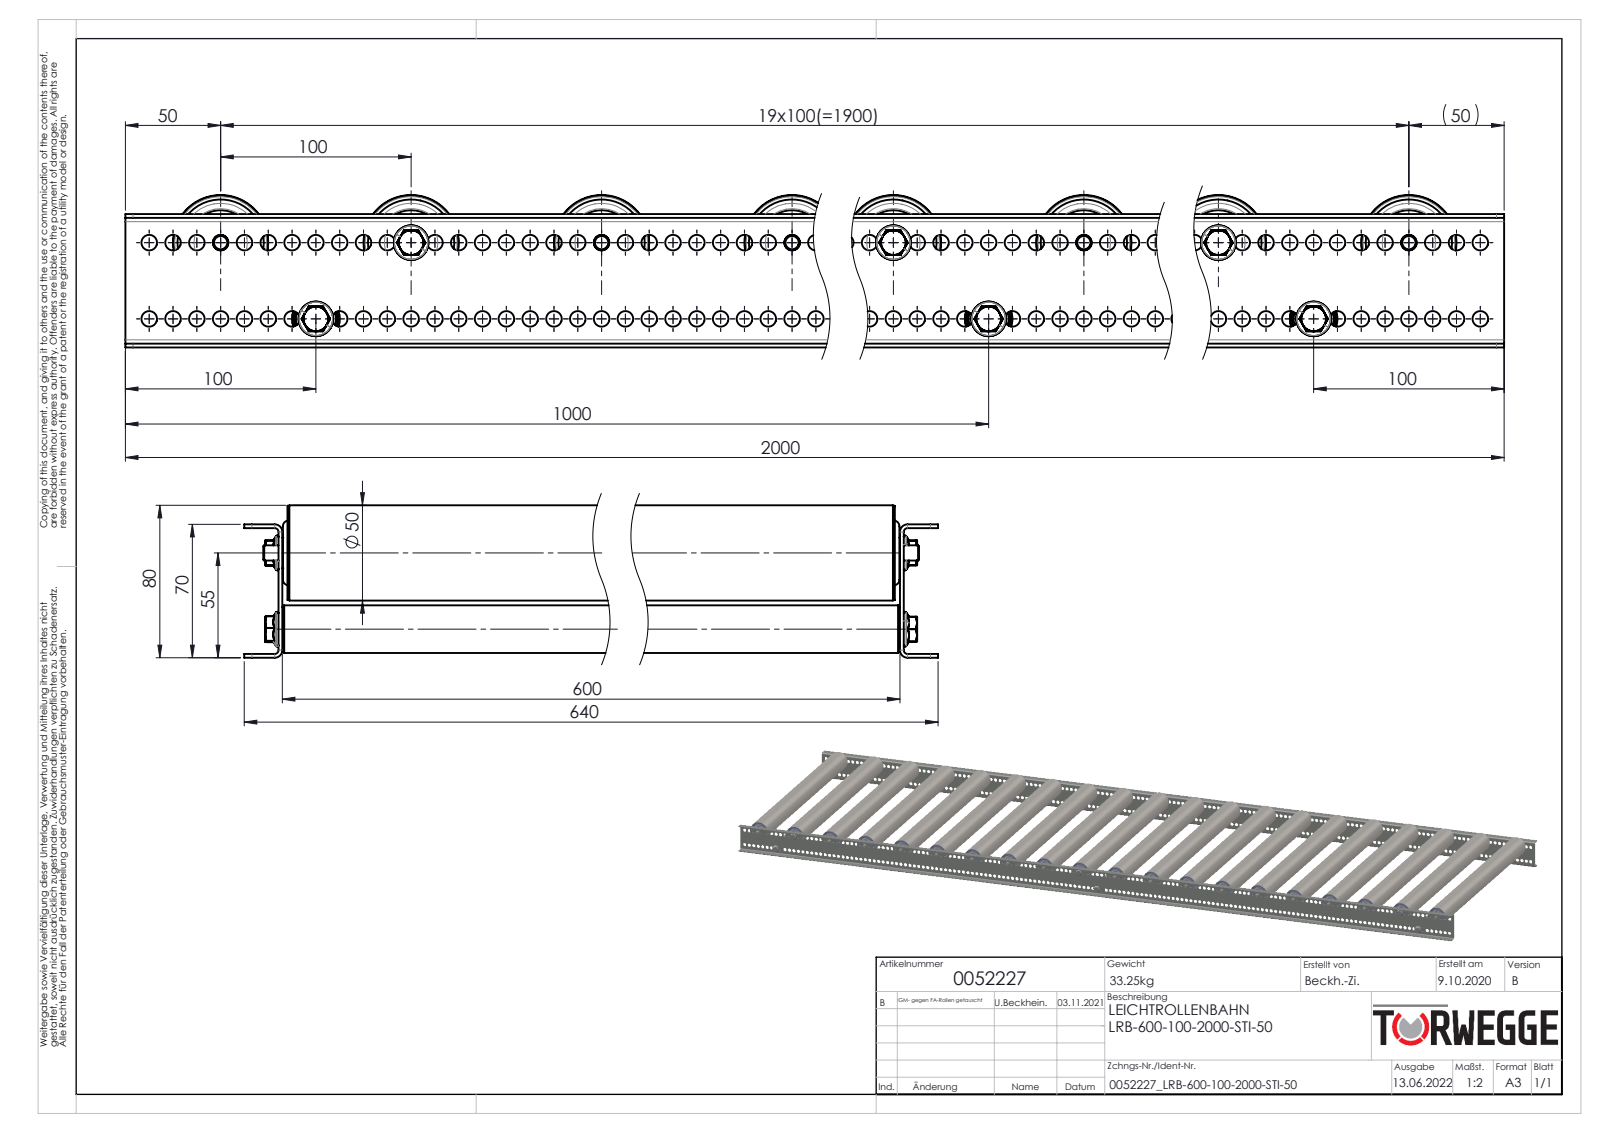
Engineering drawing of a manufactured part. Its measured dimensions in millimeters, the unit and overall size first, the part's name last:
Units: millimetres
Overall size (bounding box): 2000 × 640 × 80
Round holes (diameter × count): ⌀8.2 ×318, ⌀17.1 ×20, ⌀18.5 ×20, ⌀27.7 ×20, ⌀45.3 ×20, ⌀47 ×20, ⌀7.6 ×17, ⌀6.8 ×6, ⌀12 ×3, ⌀12.2 ×3, ⌀19.2 ×3, ⌀21 ×3
Round bosses / shafts (diameter × count): ⌀8 ×23, ⌀50 ×20, ⌀49.5 ×20, ⌀47.3 ×20, ⌀29.7 ×20, ⌀27.4 ×20, ⌀27.3 ×20, ⌀16 ×20
Partial cylindrical surfaces — rounded edges, fillets, slot ends (radius × count): R0.6 ×34, R0.75 ×34, R2.45 ×34, R4.87 ×17, R7 ×17, R2.5 ×12, R4 ×8, R2 ×4
Main face-to-face distances: 2, 602, 68, 600, 604, 70, 66, 1, 2.3, 601.7
Hole centre spacings: 12.5, 25, 37.5, 50, 62.5, 75, 87.5, 100
Volume: 4 862 000 mm³ · Surface area: 5 622 000 mm²
Bodies: 476 solids, 8806 faces (1716 planar, 3328 cylindrical, 3762 other)
Part name (STEP PRODUCT): 0039780-Achse-ST-Ø12-KFG_IGM8-AL=600-TRG; 0024178_Passscheibe_DIN988_12x18x1; 0026293_Typ-TRG-50x1,5-12; Druckfeder_1,2x10x30 (+8 more)
STEP written by: SolidWorks 2020 (AUTOMOTIVE_DESIGN)
